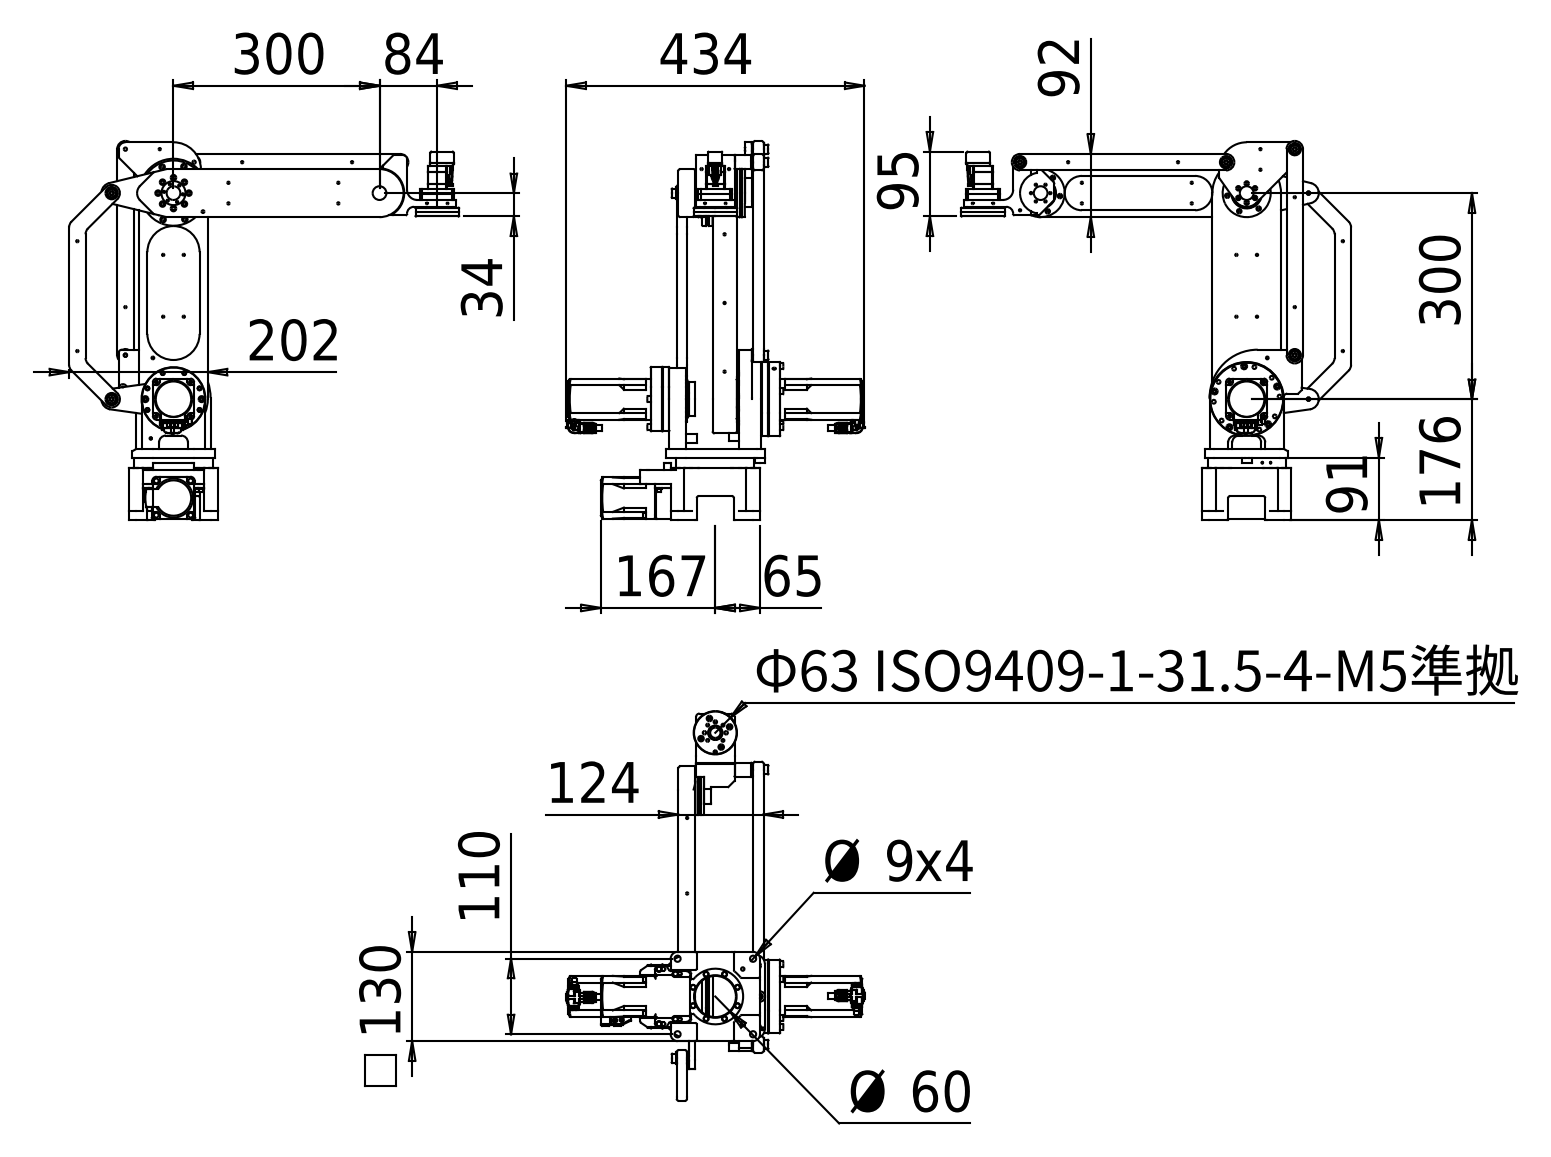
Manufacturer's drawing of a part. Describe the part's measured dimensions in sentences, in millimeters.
The part is named "DGB130R36-AZACL_MovingPart^DGB130_L; hexagon socket head cap screw_jis_JIS B 1176 M6 x 10 (10) --N; DGB130_L; outside_CSG-25-xxx-2UH-LW-SP-A_fixed.STEP (+8 more)". Its 3-D file was written by "SolidWorks 2022 (AUTOMOTIVE_DESIGN)". It is 313 solids with 11681 faces: 4414 planar, 3809 cylindrical and 3458 other. Overall it measures 629.63 by 560.29 by 434.8 millimeters. Its volume is 5 247 000 cubic millimeters and its surface area 1 091 000 square millimeters. Round holes: 54 of diameter 3.3, 54 of diameter 4.2, 46 of diameter 5, 37 of diameter 4.5, 32 of diameter 3.4, 27 of diameter 8, 26 of diameter 5.5, 26 of diameter 6.5, 22 of diameter 2.5, 22 of diameter 3, 16 of diameter 6.6, 16 of diameter 11. Round bosses or shafts: 79 of diameter 4, 48 of diameter 3.2, 43 of diameter 6, 40 of diameter 7, 34 of diameter 5.5, 34 of diameter 3, 26 of diameter 4.8, 22 of diameter 8.5. Partial cylindrical surfaces (rounded edges, fillets, slot ends): 98 of radius 0.3, 73 of radius 0.2, 46 of radius 3, 42 of radius 2, 41 of radius 1, 23 of radius 2.62, 23 of radius 2.64, 23 of radius 3.08. The main face-to-face distances are 35, 27, 15, 25, 60, 12, 74, 39, 24, 109. The hole center spacings are 6.72, 23.39, 52, 4.86, 18.61, 21.1, 50, 12.
